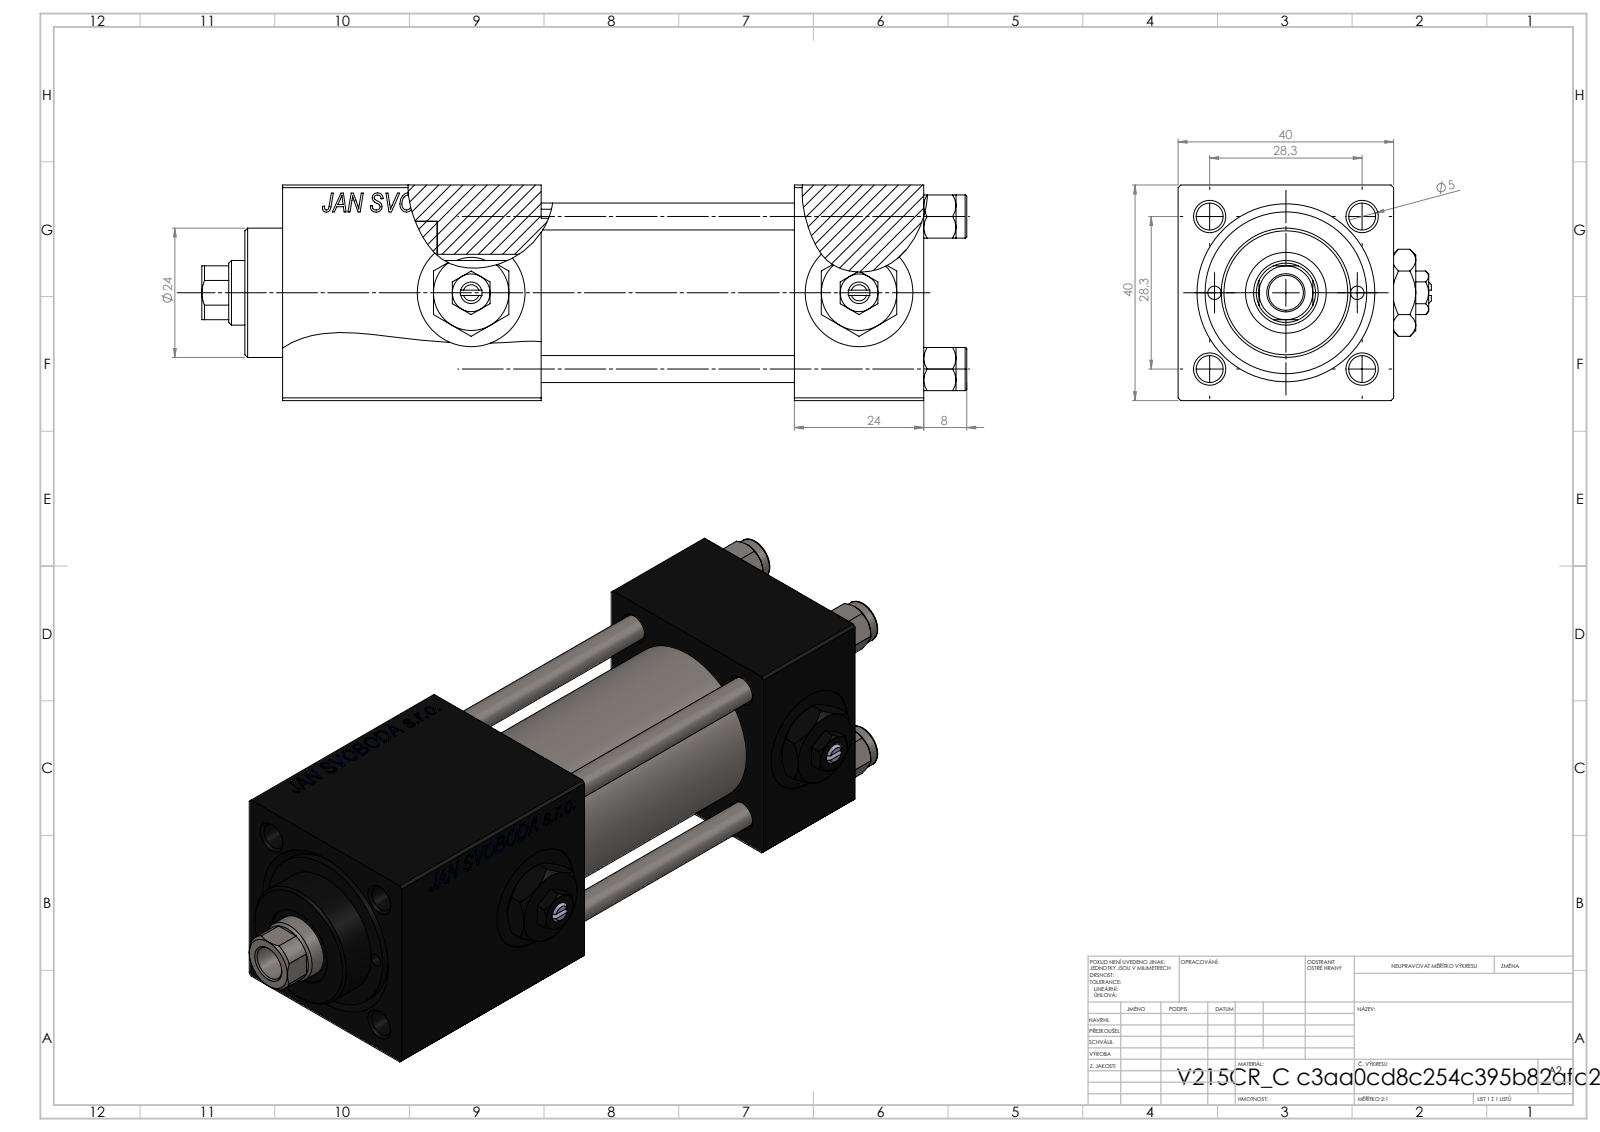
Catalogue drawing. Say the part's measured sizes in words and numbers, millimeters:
The part is named "V215CR_C_Body; V215_VC_A; V215CR_VCP_C; Zatka_pro_OIL_PORT (+2 more)". Its 3-D file was written by "SolidWorks 2019 (CONFIG_CONTROL_DESIGN)". It is 13 solids with 1254 faces: 574 planar, 102 cylindrical and 578 other. Overall it measures 142 by 47 by 40 millimeters. Its volume is 140 936 cubic millimeters and its surface area 56 288 square millimeters. Round holes: 4 of diameter 5, 3 of diameter 20, 2 of diameter 2.5, 2 of diameter 7, 2 of diameter 13.16, 1 of diameter 6.5, 1 of diameter 12, 1 of diameter 15, 1 of diameter 25, 1 of diameter 30. Round bosses or shafts: 4 of diameter 8, 1 of diameter 31, 1 of diameter 24. Partial cylindrical surfaces (rounded edges, fillets, slot ends): 1 of radius 5.5. The main face-to-face distances are 40, 24, 39.8, 90.3, 66.3, 47, 48, 71, 19.3, 95. The hole center spacings are 14.18, 20.01, 28.3, 30.84, 13.25, 40.02, 26.5, 72.
